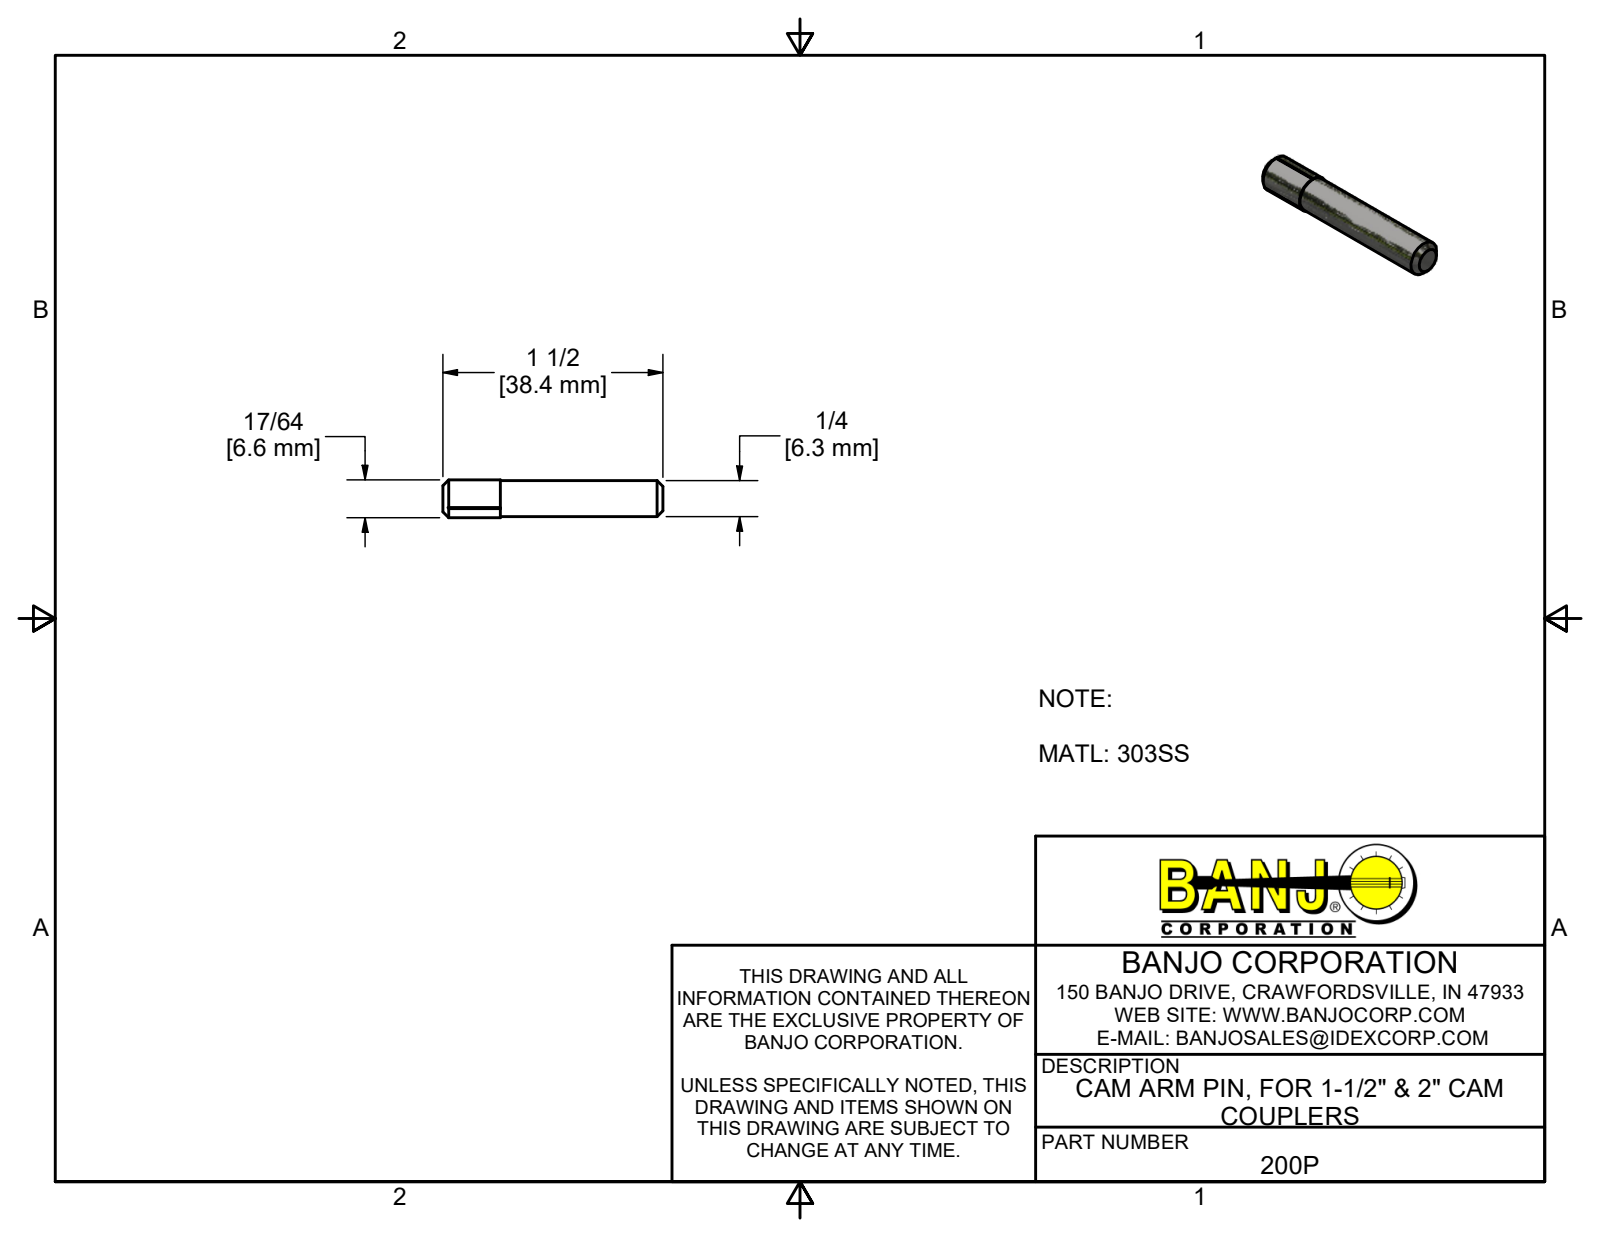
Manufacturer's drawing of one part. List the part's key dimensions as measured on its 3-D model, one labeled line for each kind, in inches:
Part name (STEP PRODUCT): 200P
STEP written by: Autodesk Inventor 2022 (AUTOMOTIVE_DESIGN)
Units: inches
Bodies: 1 solid, 17 faces (11 planar, 4 cylindrical, 2 other)
Overall size (bounding box): 1.512 × 0.26 × 0.26
Volume: 0.074 in³ · Surface area: 1.268 in²
Round bosses / shafts (diameter × count): ⌀0.26 ×1, ⌀0.249 ×1
Main face-to-face distances: 1.512, 0.393, 1.119
